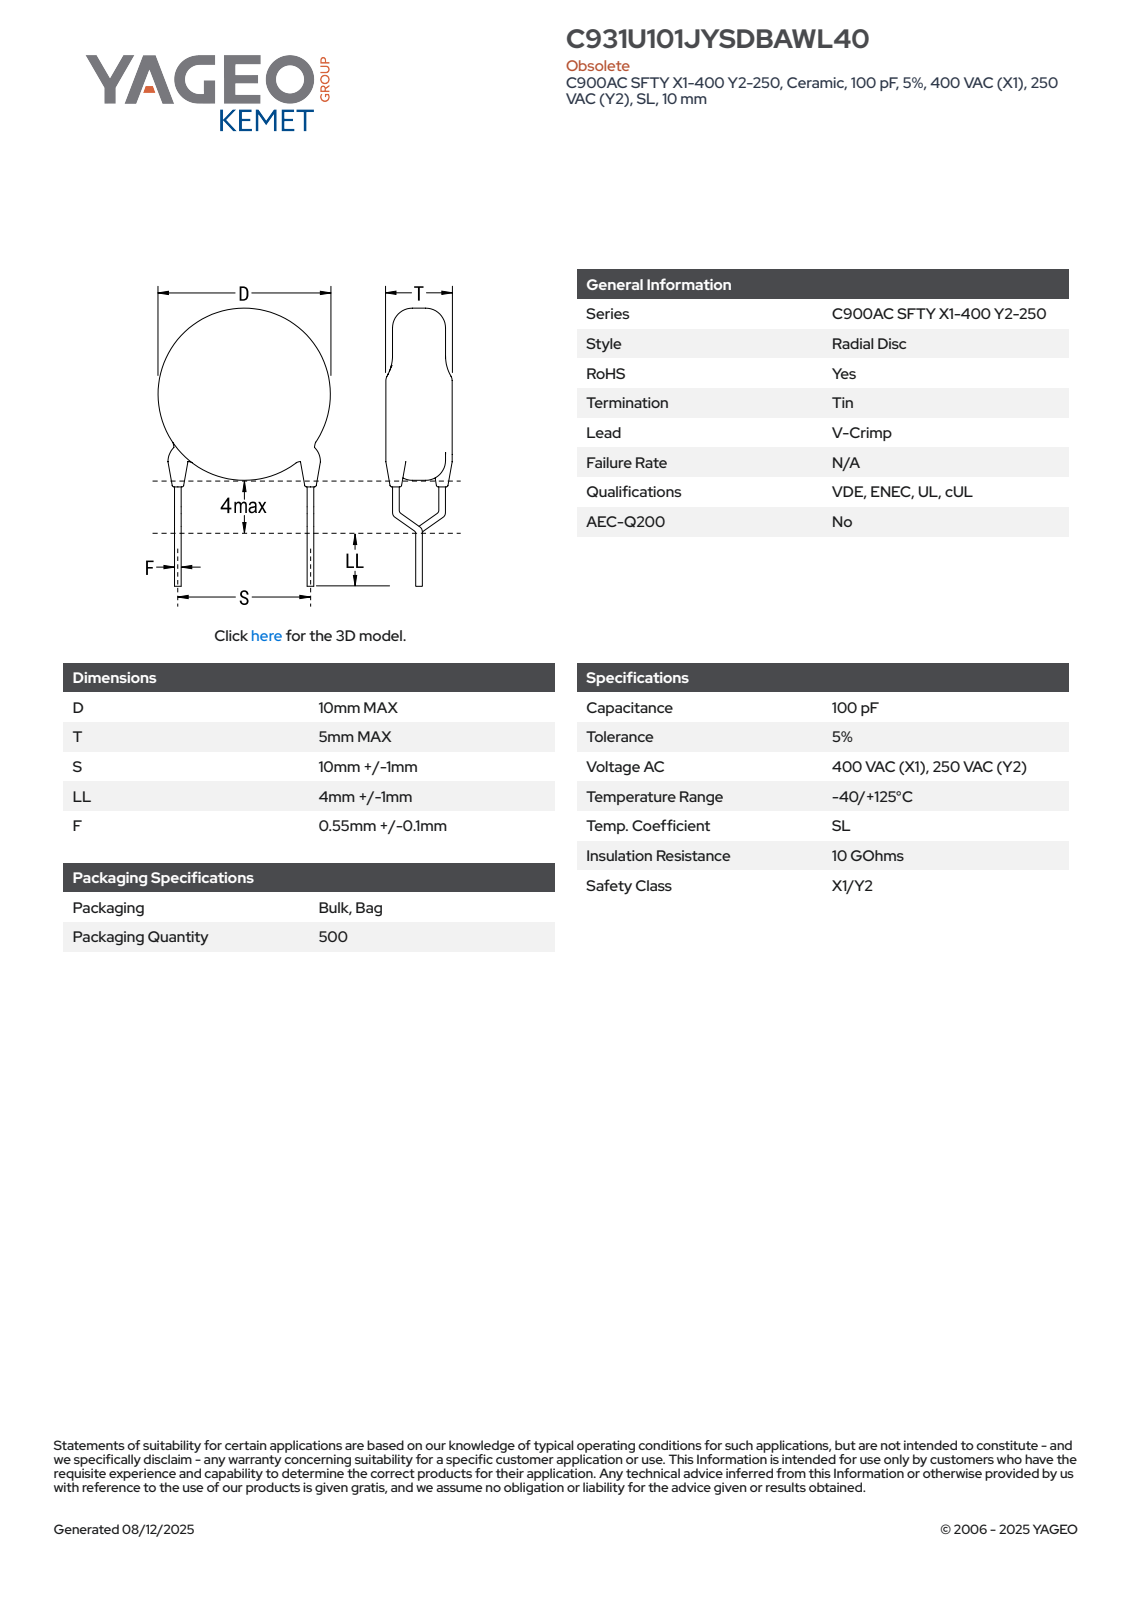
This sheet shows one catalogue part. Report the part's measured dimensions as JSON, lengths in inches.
{"part_name": "CCD_VCC900_D10T5S10LL5F0.65", "step_written_by": "SolidWorks 2014 (AUTOMOTIVE_DESIGN)", "units": "inches", "bodies": {"solids": 5, "faces": 93, "planar": 65, "cylindrical": 16, "other": 12}, "overall_size": [0.74, 0.419, 0.197], "volume_in3": 0.024, "surface_area_in2": 0.539, "round_bosses_or_shafts": [[0.026, 6], [0.394, 1]], "face_to_face_distances": [0.197, 0.311, 0.051, 0.569, 0.258, 0.518, 0.207, 0.013, 0.041, 0.106]}
